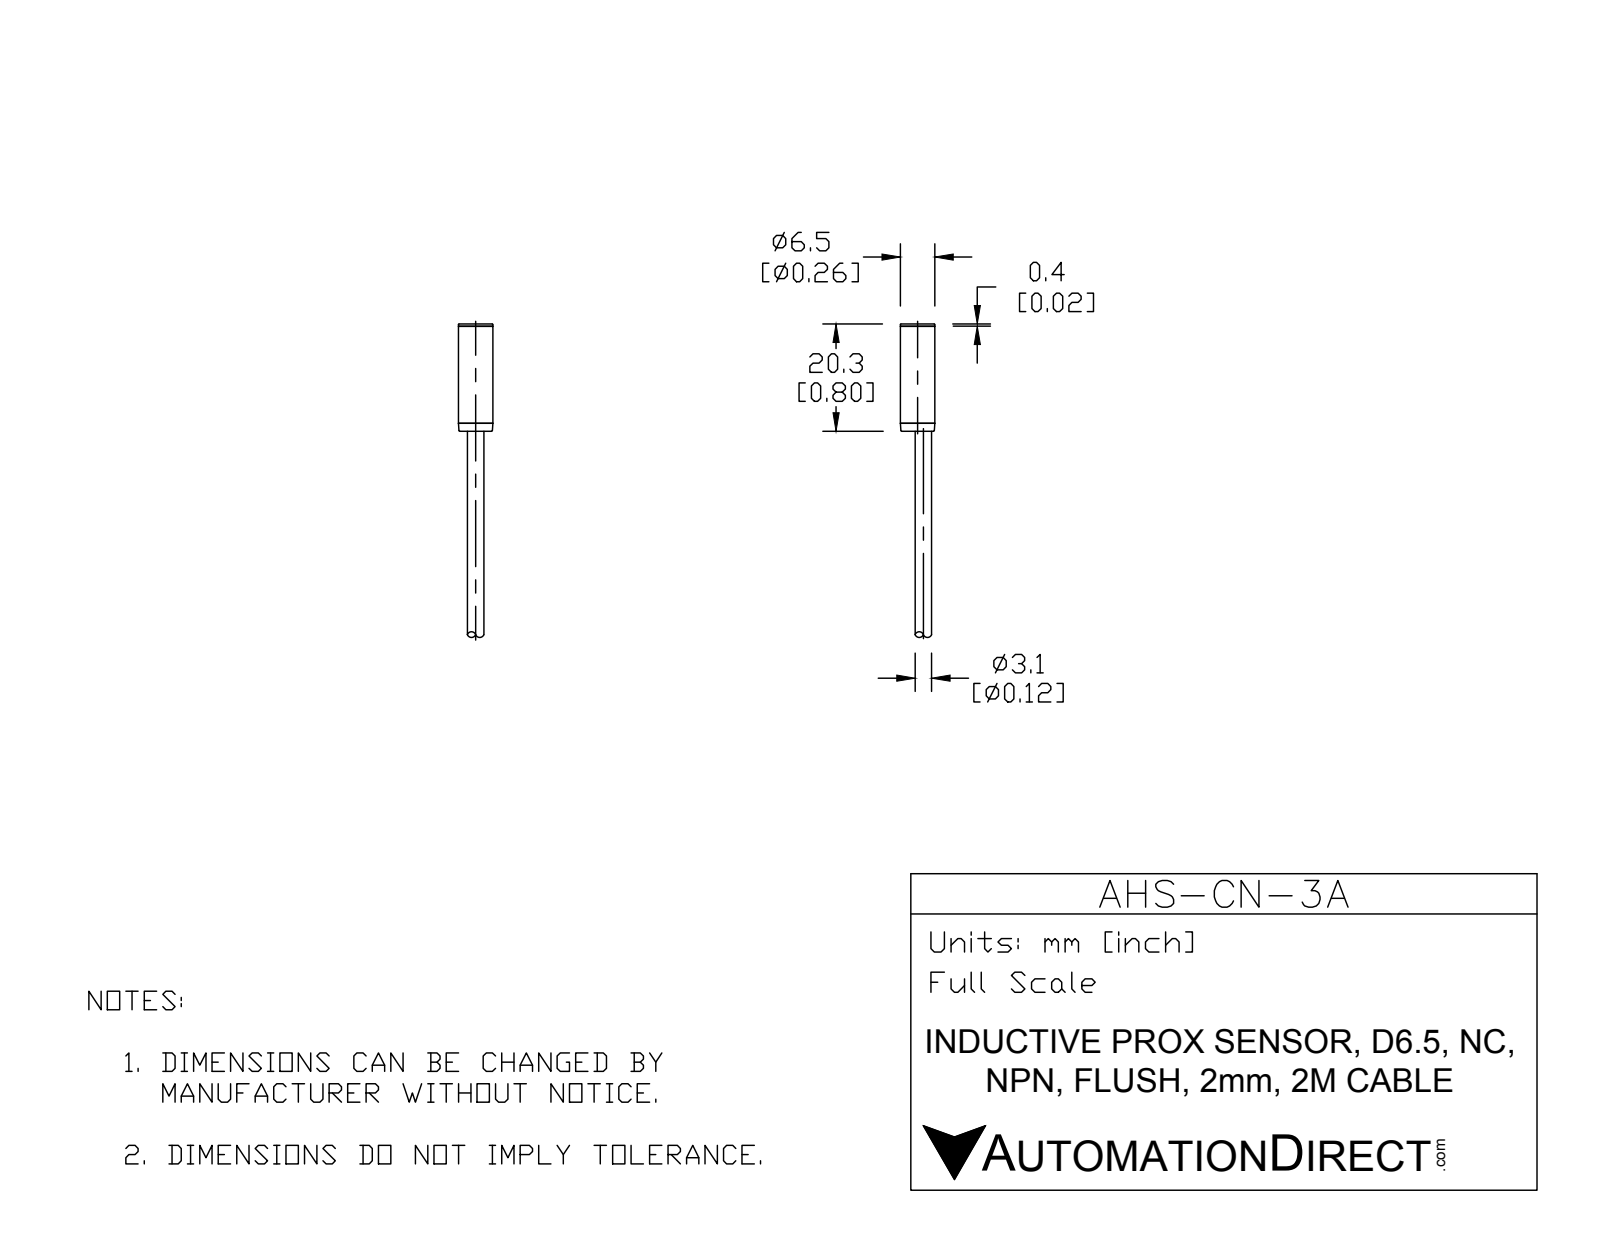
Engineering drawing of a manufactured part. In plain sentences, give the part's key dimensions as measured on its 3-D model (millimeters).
The part is named "AHS-CN-3A". Its 3-D file was written by "SolidWorks 2015 (CONFIG_CONTROL_DESIGN)". It is 2 solids with 17 faces: 5 planar, 6 cylindrical and 6 other. Overall it measures 70.3 by 6.5 by 6.5 millimeters. Its volume is 1 050 cubic millimeters and its surface area 979 square millimeters. Round bosses or shafts: 1 of diameter 6.5, 1 of diameter 3.1. The main face-to-face distances are 20.3, 50, 70.3, 69.9, 19.9, 0.4.
